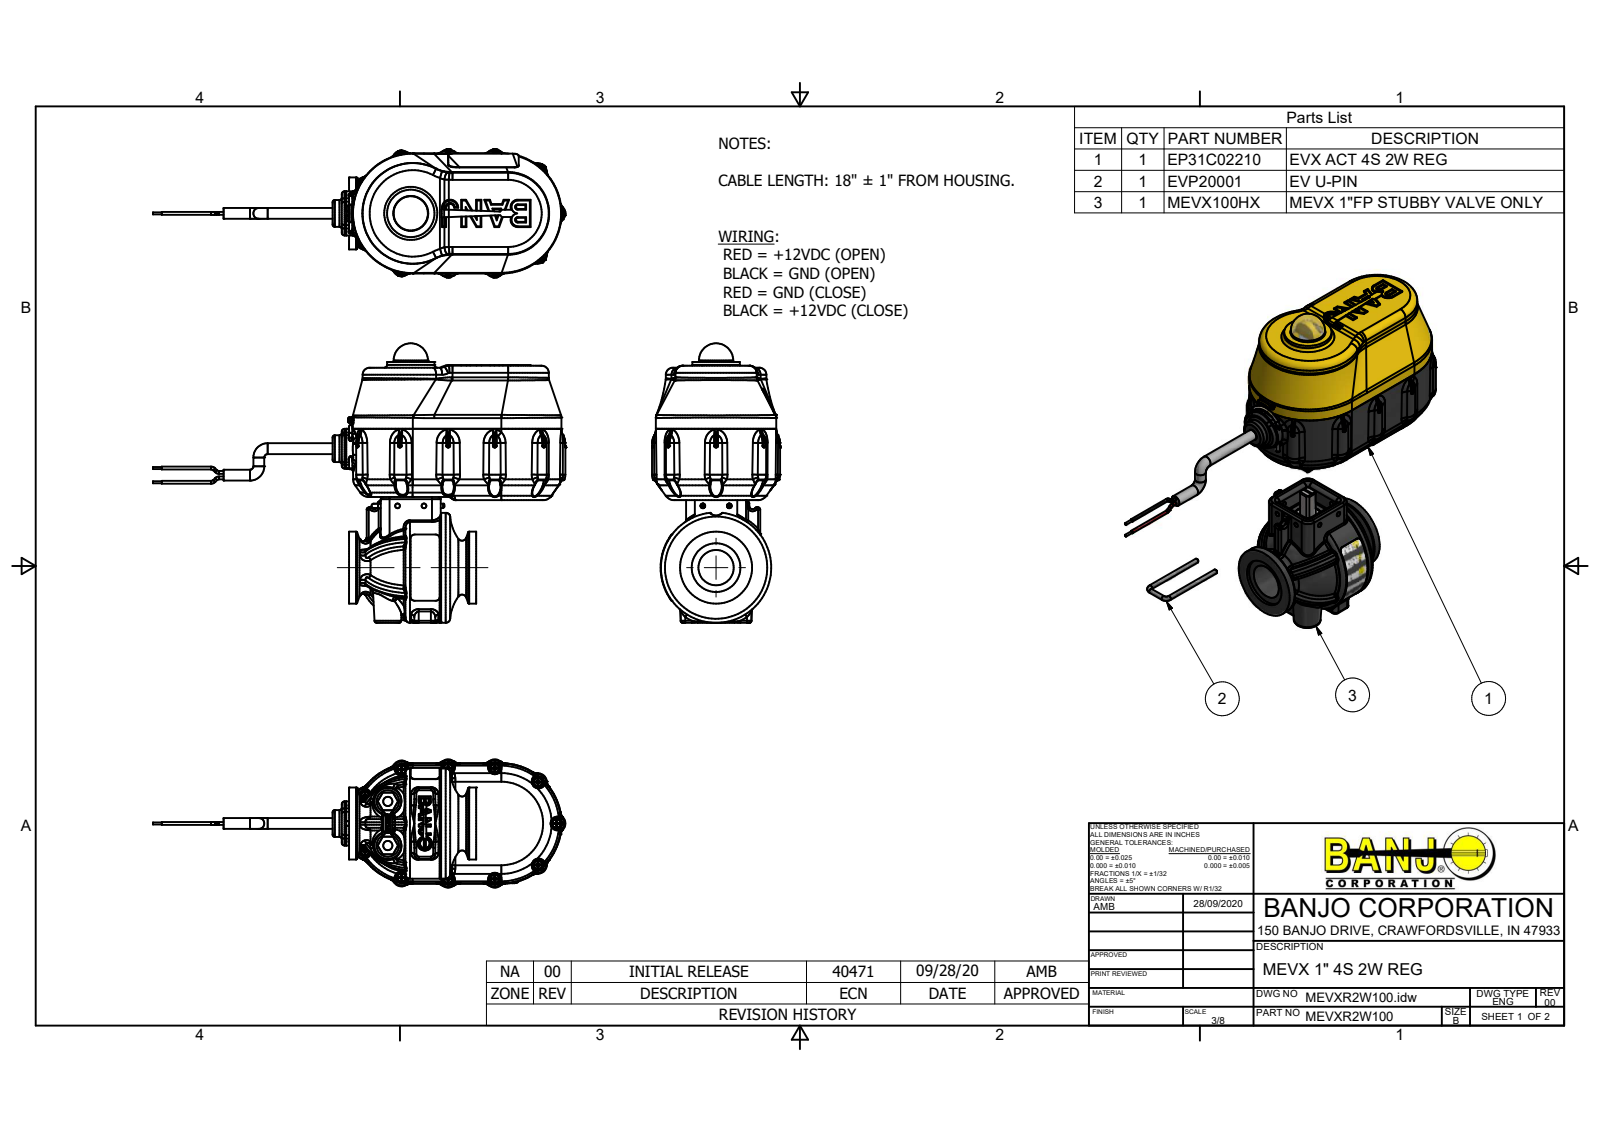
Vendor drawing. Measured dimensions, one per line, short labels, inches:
name: MEVXR2W100; EP31C02210; 91400A119; 95584A200 (+8 more)
written by: Autodesk Inventor 2019 (AUTOMOTIVE_DESIGN)
unit: in
bodies: 83 solids, 12235 faces (3708 planar, 3073 cylindrical, 5454 other)
size: 11.685 × 7.916 × 3.63
volume: 45.34 in³; area: 526.4 in²
holes: 13× ⌀0.15, 11× ⌀0.095, 5× ⌀0.135, 4× ⌀0.107, 4× ⌀0.126, 4× ⌀0.136, 4× ⌀0.17, 2× ⌀0.089, 2× ⌀0.105, 2× ⌀0.115, 2× ⌀0.118, 2× ⌀0.123
bosses: 17× ⌀0.25, 11× ⌀0.14, 11× ⌀0.108, 11× ⌀0.085, 10× ⌀0.08, 4× ⌀0.27, 4× ⌀0.219, 4× ⌀0.164
rounds: 147× R0.04, 83× R0.02, 56× R0.01, 50× R0.06, 43× R0.005, 28× R0.08, 26× R0.125, 24× R0.03
face distances: 0.1, 2.565, 1.685, 0.78, 2.465, 0.88, 0.035, 0.987, 3.005, 0.055
hole spacings: 1.79, 1.283, 1.662, 2.73, 2.967, 3.45, 0.487, 0.492
